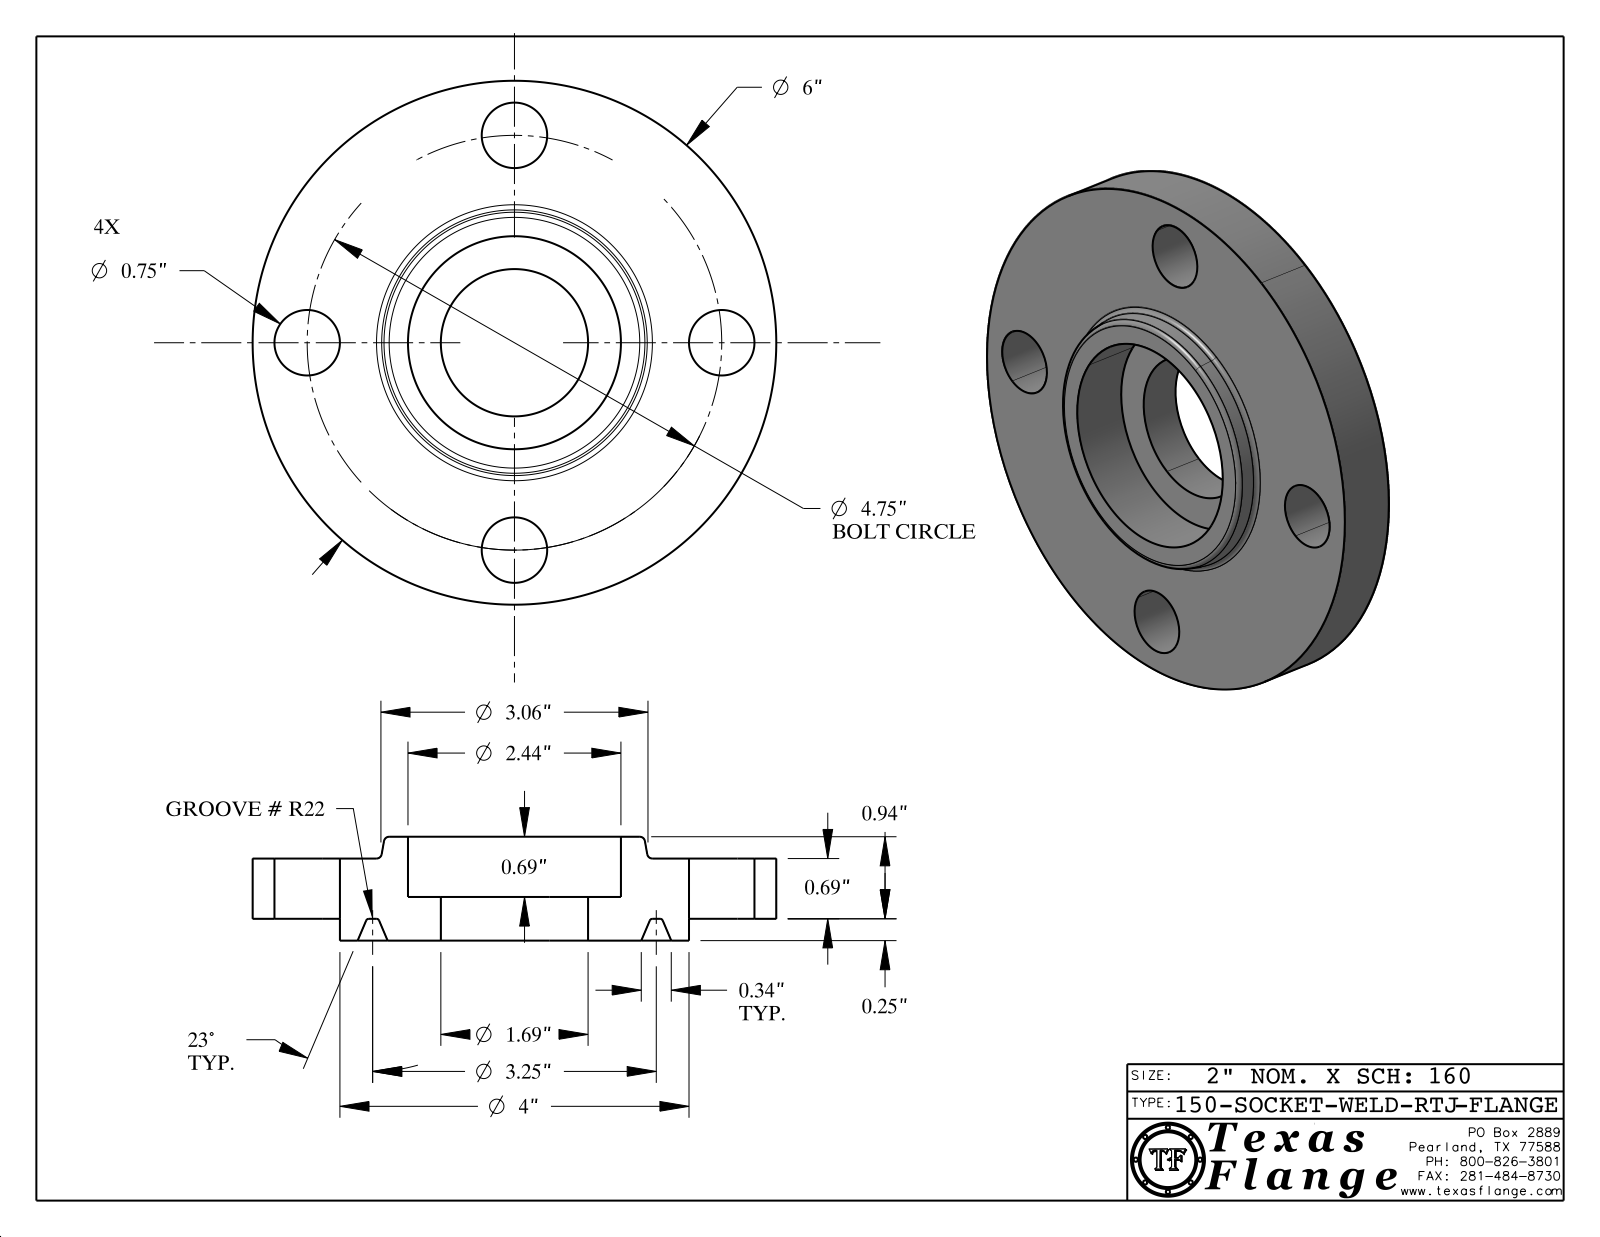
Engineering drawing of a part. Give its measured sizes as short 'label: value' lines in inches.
name: 150-SOCKET-WELD-RTJ
written by: CATIA V5 STEP AP214 (AUTOMOTIVE_DESIGN)
unit: in
bodies: 1 solid, 422 faces (372 planar, 36 cylindrical, 14 other)
size: 6 × 6 × 1.19
volume: 18.27 in³; area: 84.17 in²
holes: 4× ⌀0.75, 1× ⌀0.495, 1× ⌀1.687, 1× ⌀2.44
bosses: 8× ⌀0.03, 1× ⌀6, 1× ⌀4, 1× ⌀0.39
face distances: 0.69, 0.25, 0.94, 0.5, 0.44, 1.19, 0.925, 0.675, 0.425, 0.015
hole spacings: 2.375, 3.359, 1.818, 4.389, 4.75
